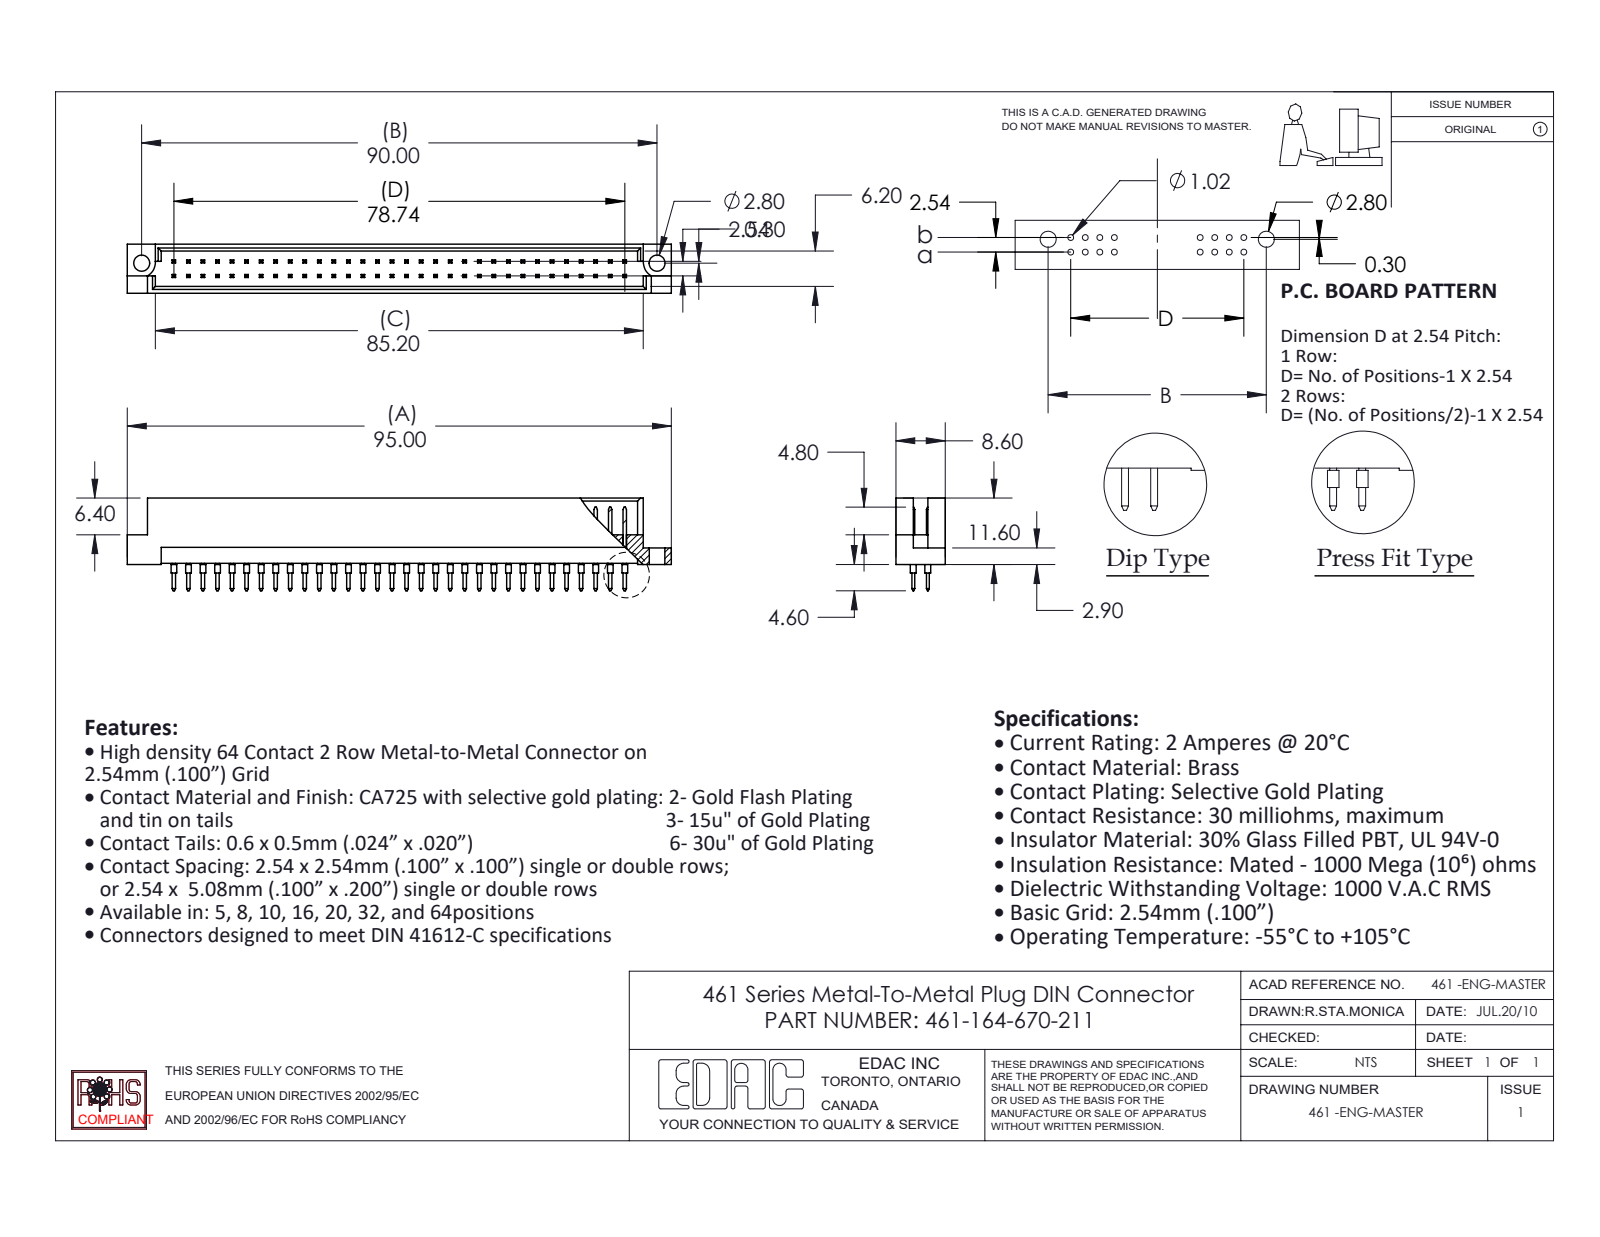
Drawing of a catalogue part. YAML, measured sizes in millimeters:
part_name: "461 Part_64; 461-290_70; 461-164-670-211"
step_written_by: "SolidWorks 2020 (CONFIG_CONTROL_DESIGN)"
units: millimeters
bodies: {solids: 65, faces: 1713, planar: 1578, cylindrical: 135, other: 0}
overall_size: [95, 16.2, 8.6]
volume: 4976
surface_area: 7855
round_holes:
  - {diameter: 2.8, count: 2}
round_bosses_or_shafts:
  - {diameter: 1, count: 64}
partial_cylinders:
  - {radius: 2.8, count: 2}
face_to_face_distances: [1.2, 7.4, 8.6, 2.54, 6.2, 3.28, 5.32, 2.08, 4.12, 2.78]
hole_center_spacings: [90]
